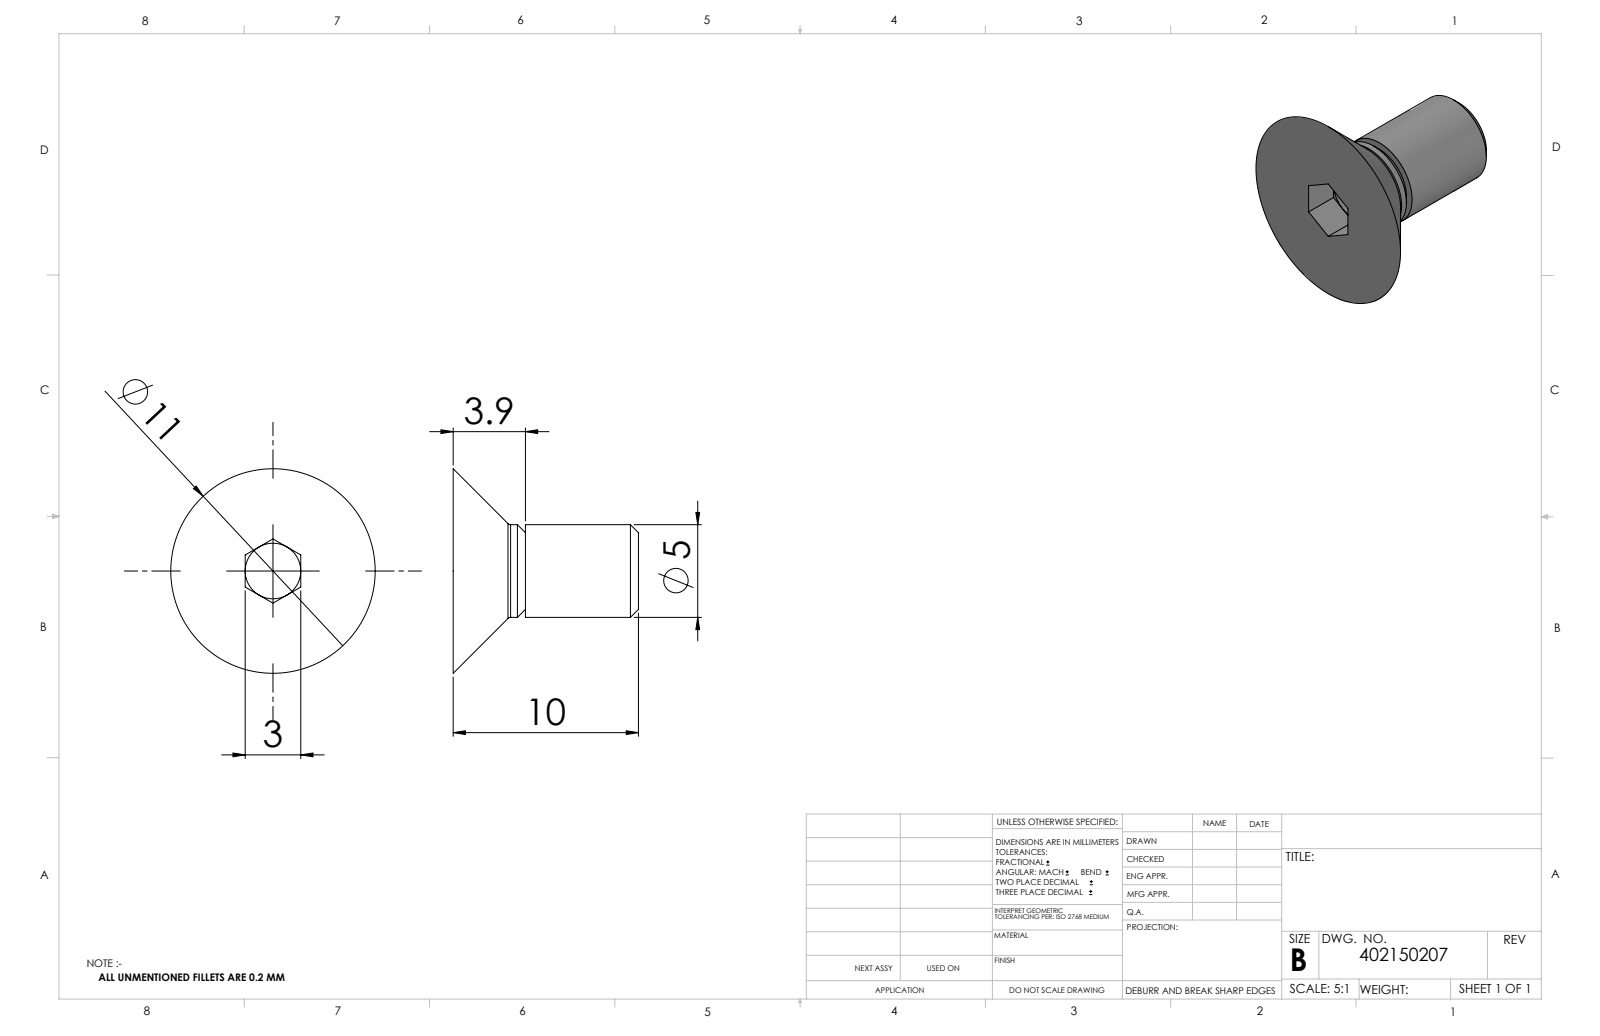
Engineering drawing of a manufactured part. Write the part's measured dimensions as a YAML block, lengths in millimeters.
part_name: "402150207_c_1"
step_written_by: "SolidWorks 2014 (CONFIG_CONTROL_DESIGN)"
units: millimeters
bodies: {solids: 1, faces: 29, planar: 15, cylindrical: 4, other: 10}
overall_size: [11.03, 11.03, 10]
volume: 277
surface_area: 357
round_bosses_or_shafts:
  - {diameter: 5, count: 1}
face_to_face_distances: [10, 3, 3.9, 6.1, 1.9, 2, 8.1]
